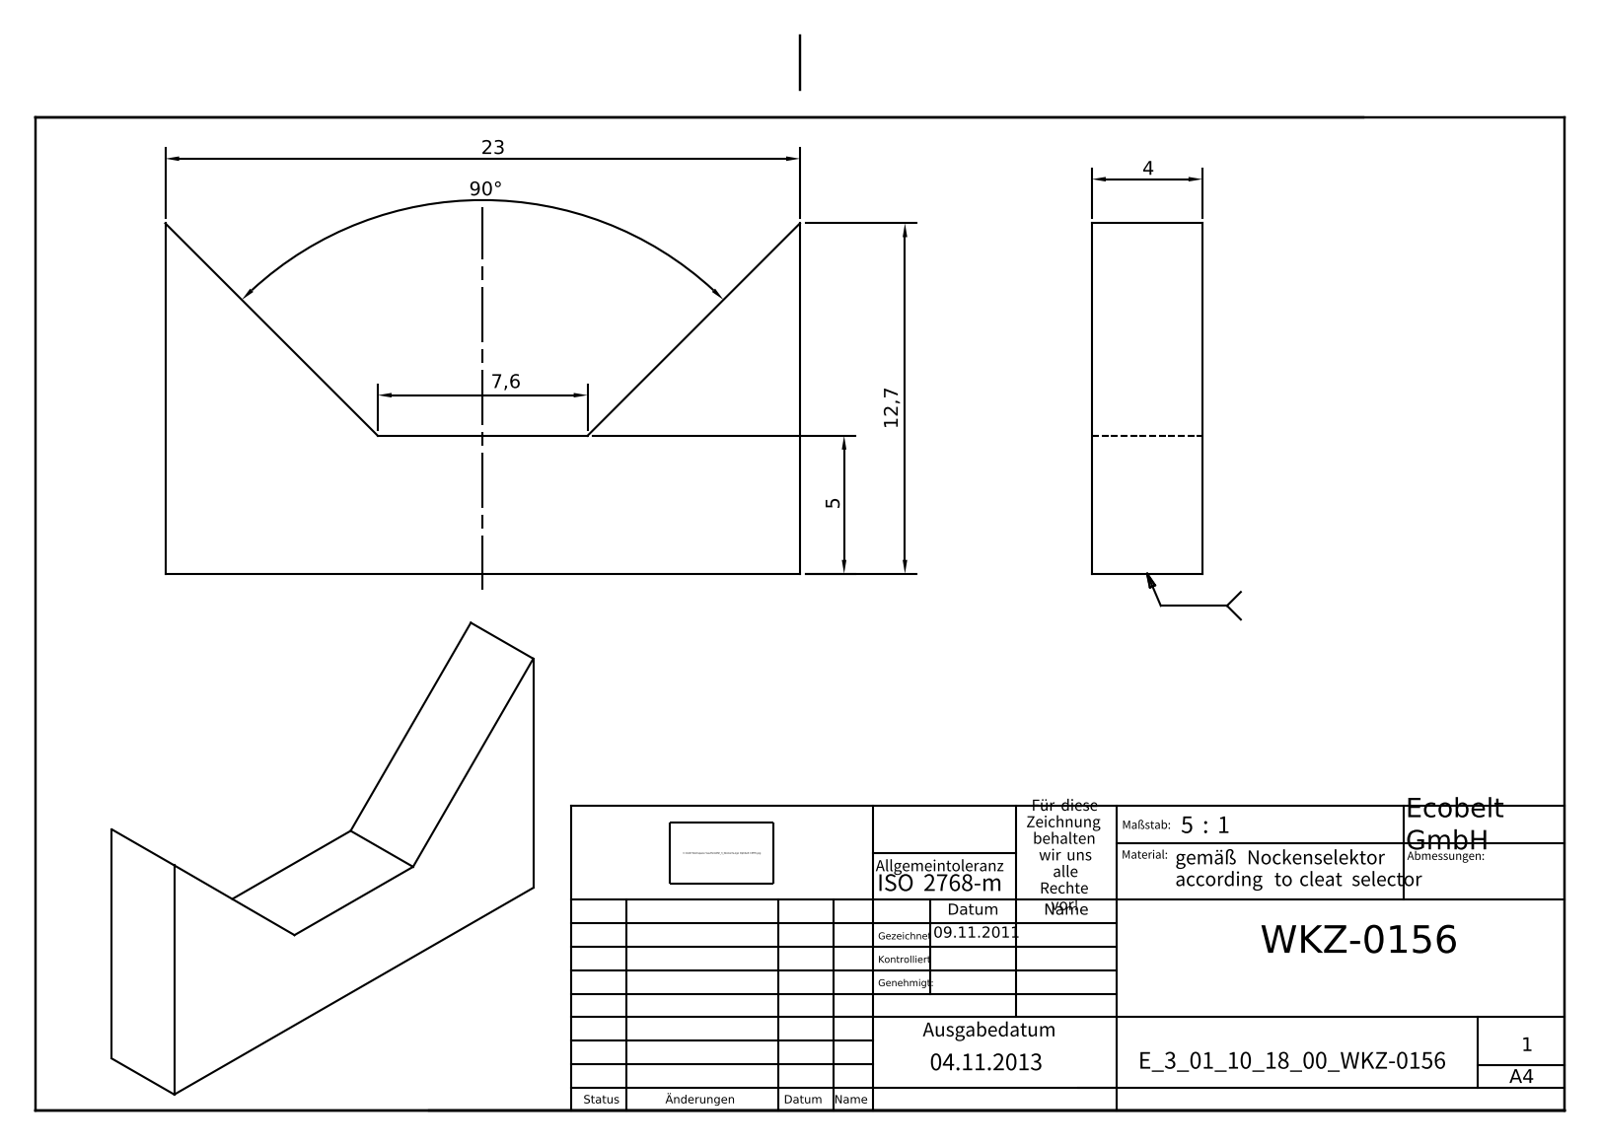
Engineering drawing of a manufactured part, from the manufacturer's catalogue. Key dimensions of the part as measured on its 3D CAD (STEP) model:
Part name (STEP PRODUCT): E_3_01_10_18_00_WKZ-0156
STEP written by: Autodesk Inventor 2025 (AUTOMOTIVE_DESIGN)
Units: millimetres
Bodies: 1 solid, 8 faces (8 planar, 0 cylindrical, 0 other)
Overall size (bounding box): 23 × 12.7 × 4
Volume: 697 mm³ · Surface area: 660 mm²
Main face-to-face distances: 4, 23, 5
